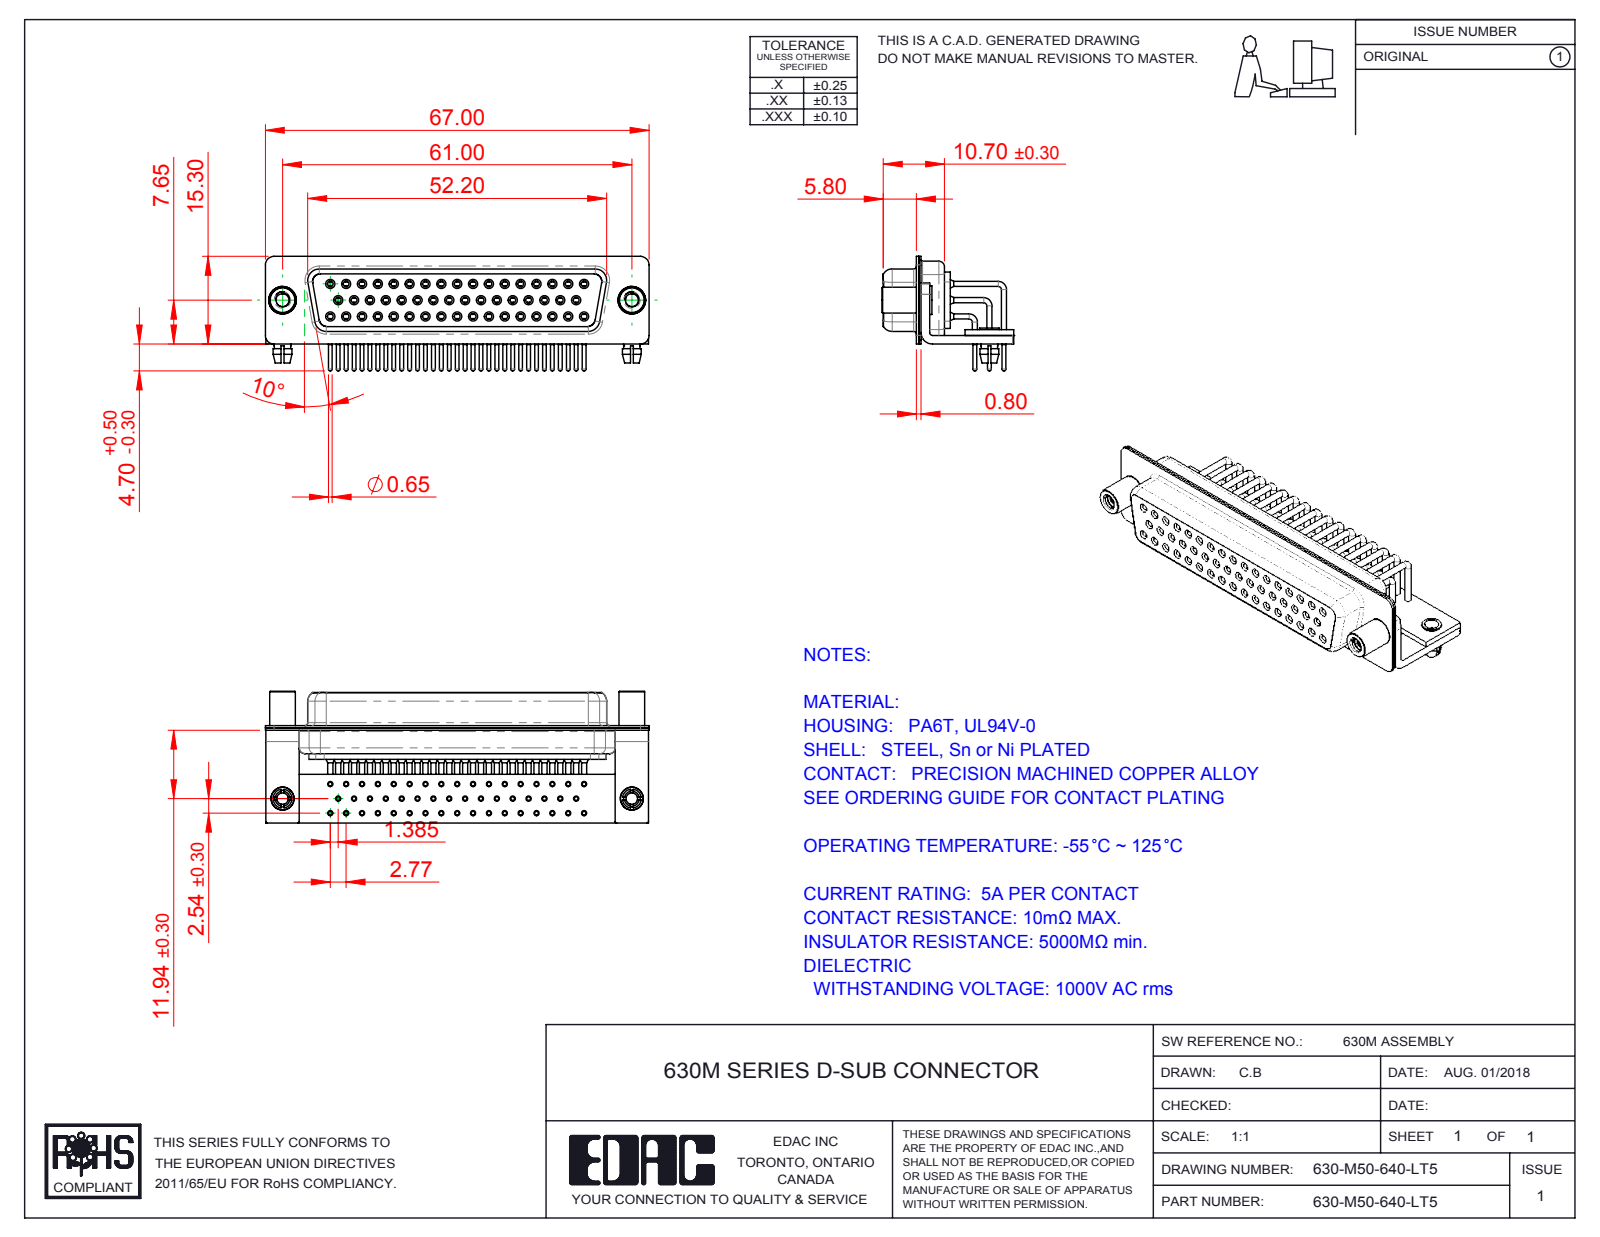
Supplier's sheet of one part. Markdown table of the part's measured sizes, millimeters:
| quantity | value |
| --- | --- |
| part name | 630M Contact Row 1_50 Contacts; 630M Shell Rear_50 Contacts; 630M Shell Front_50 Contacts; 630M Housing_50 Contacts (+7 more) |
| STEP written by | SolidWorks 2016 (CONFIG_CONTROL_DESIGN) |
| units | millimeters |
| bodies | 60 solids, 3221 faces (893 planar, 1483 cylindrical, 845 other) |
| overall size | 67 × 23 × 20 |
| volume | 8 037 mm³ |
| surface area | 19 165 mm² |
| round holes (diameter × count) | 2 × 52, 0.9 × 50, 1 × 50, 1.1 × 50, 1.7 × 50, 1.8 × 50, 2.26 × 2, 2.5 × 2, 3.2 × 2, 4 × 2, 4.8 × 2 |
| round bosses / shafts (diameter × count) | 0.9 × 59, 1.6 × 50, 1.5 × 50, 0.65 × 50, 5 × 2, 4.9 × 2, 4.5 × 2, 4 × 2 |
| partial cylindrical surfaces (radius × count) | 0.25 × 16, 1.5 × 16, 2 × 13, 1.35 × 8, 1.6 × 8, 0.5 × 5, 0.6 × 4, 0.65 × 4 |
| main face-to-face distances | 0.4, 1, 2.2, 0.85, 1.35, 11.85, 12.25, 5.8, 0.8, 5.9 |
| hole center spacings | 2.77, 5.54, 8.31, 11.08, 13.85, 16.62, 3.16, 19.39 |
